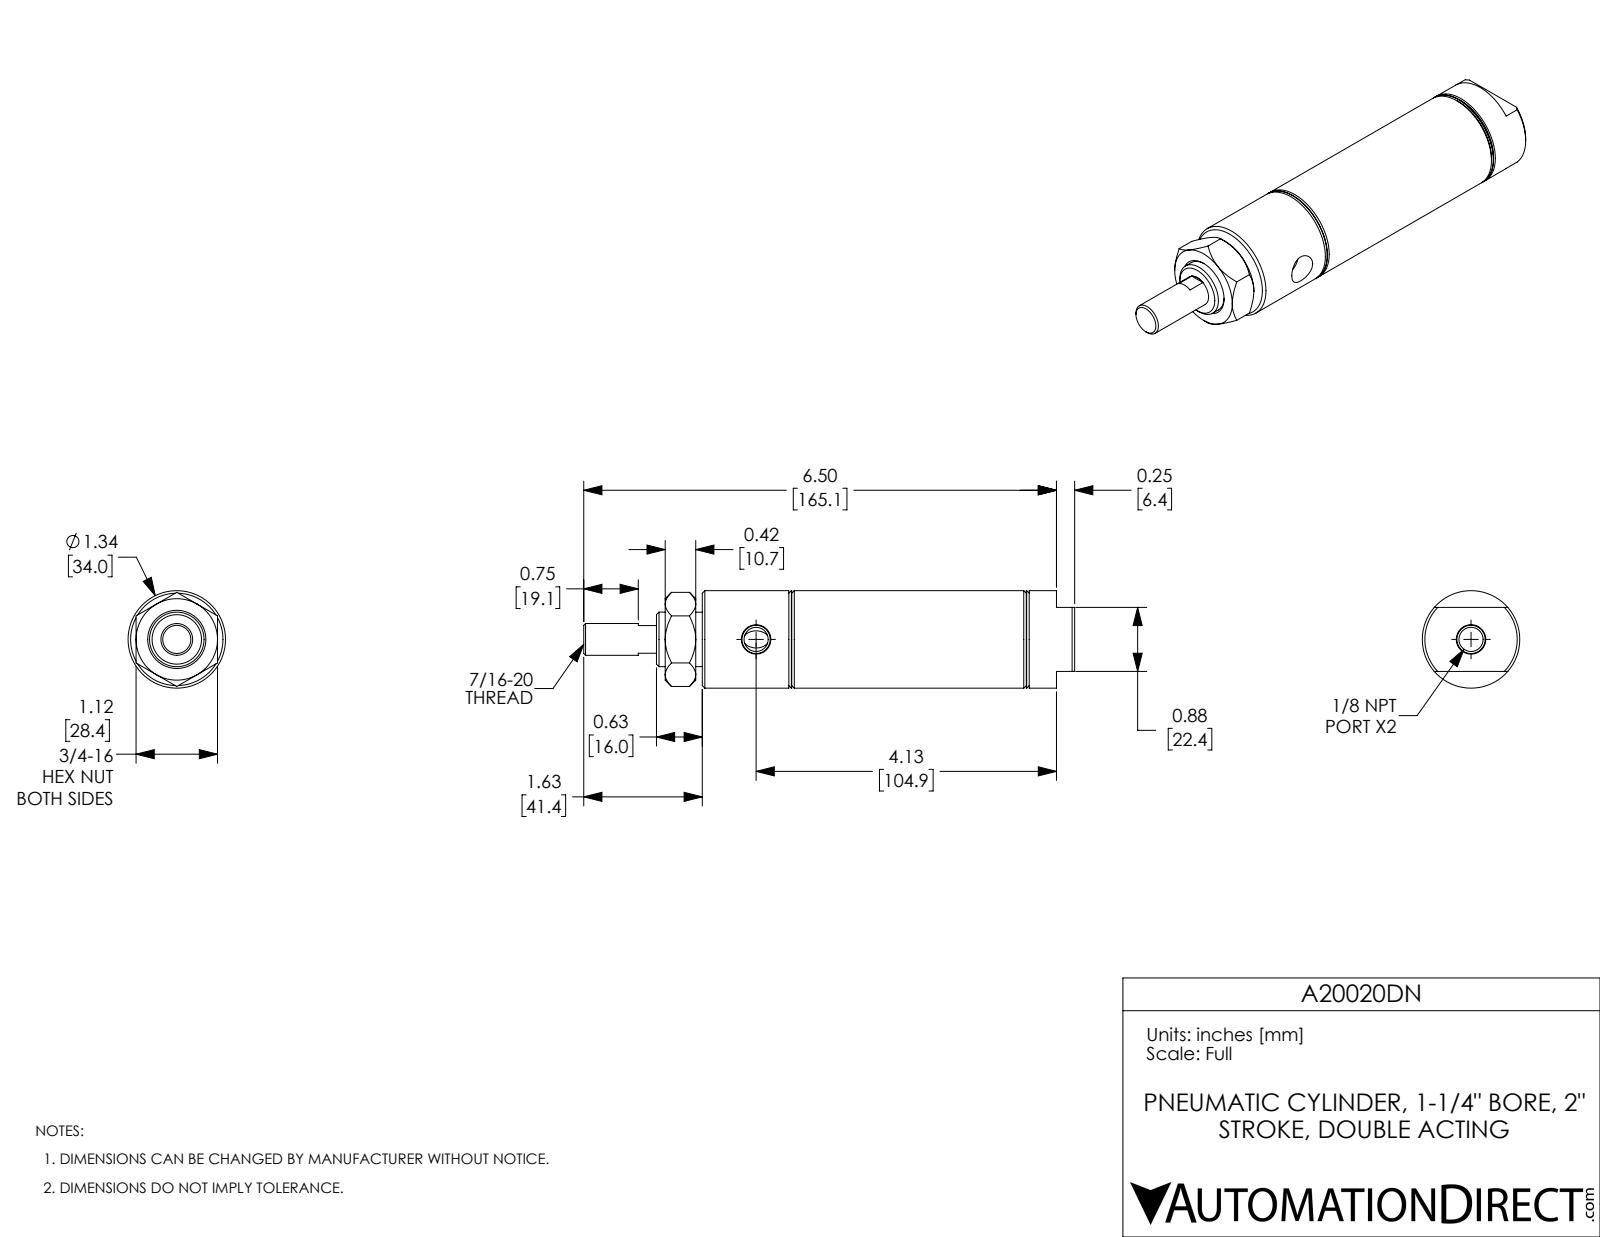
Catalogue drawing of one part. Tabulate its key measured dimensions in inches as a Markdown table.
| quantity | value |
| --- | --- |
| part name | A20020DN-Rod; A20020DN-MainBody; A20020DN; A20020DN_Mounting Nut_D-3556 |
| STEP written by | SolidWorks 2017 (AUTOMOTIVE_DESIGN) |
| units | inches |
| bodies | 3 solids, 100 faces (33 planar, 28 cylindrical, 39 other) |
| overall size | 6.75 × 1.34 × 1.34 |
| volume | 5.487 in³ |
| surface area | 57.55 in² |
| round holes (diameter × count) | 0.332 × 2, 0.437 × 1, 0.75 × 1, 1.25 × 1 |
| round bosses / shafts (diameter × count) | 1.34 × 1, 0.747 × 1 |
| main face-to-face distances | 2.5, 0.5, 2, 1.31, 1.81, 3.81, 5.12, 3.81, 3.31, 1.31 |
